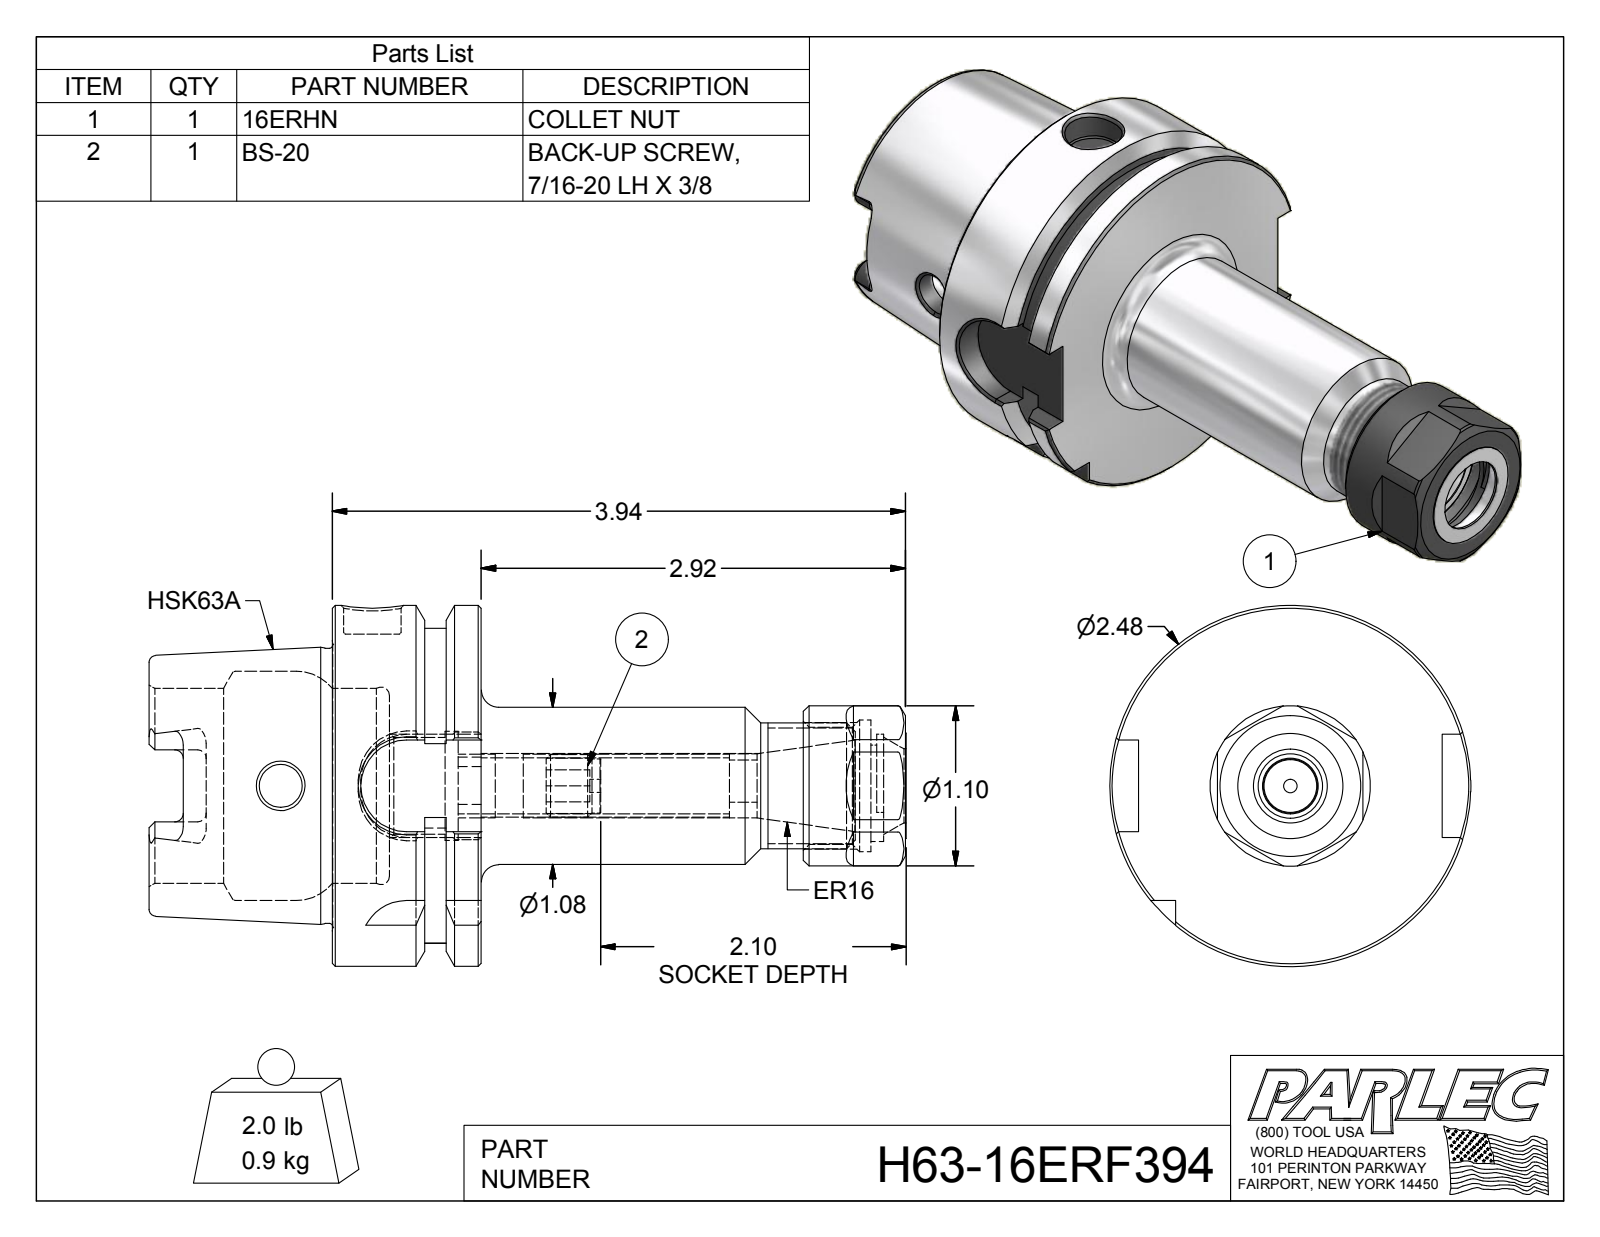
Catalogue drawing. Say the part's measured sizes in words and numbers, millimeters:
The part is named "H63-16ERF394; H63-16ER4-1; 16ERHN; BS-20". Its 3-D file was written by "Autodesk Inventor 2012 (AUTOMOTIVE_DESIGN)". It is 3 solids with 189 faces: 84 planar, 46 cylindrical and 59 other. Overall it measures 132.2 by 63 by 63 millimeters. Its volume is 115 300 cubic millimeters and its surface area 33 850 square millimeters. Round holes: 1 of diameter 2.3, 1 of diameter 7.5, 1 of diameter 9.7, 1 of diameter 10, 1 of diameter 11.2, 1 of diameter 12.9, 1 of diameter 16.8, 1 of diameter 16.9, 1 of diameter 19, 1 of diameter 20.5, 1 of diameter 23, 1 of diameter 34. Round bosses or shafts: 1 of diameter 63, 1 of diameter 48, 1 of diameter 28, 1 of diameter 27.4, 1 of diameter 22, 1 of diameter 18.4, 1 of diameter 11, 1 of diameter 9.5. Partial cylindrical surfaces (rounded edges, fillets, slot ends): 6 of radius 1.5, 4 of radius 2.9, 4 of radius 8, 1 of radius 4.9, 1 of radius 9, 1 of radius 27.5. The main face-to-face distances are 26, 6.1, 9.9, 10, 16, 32, 42, 58, 51.9, 19.9. The hole center spacings are 1.3.
